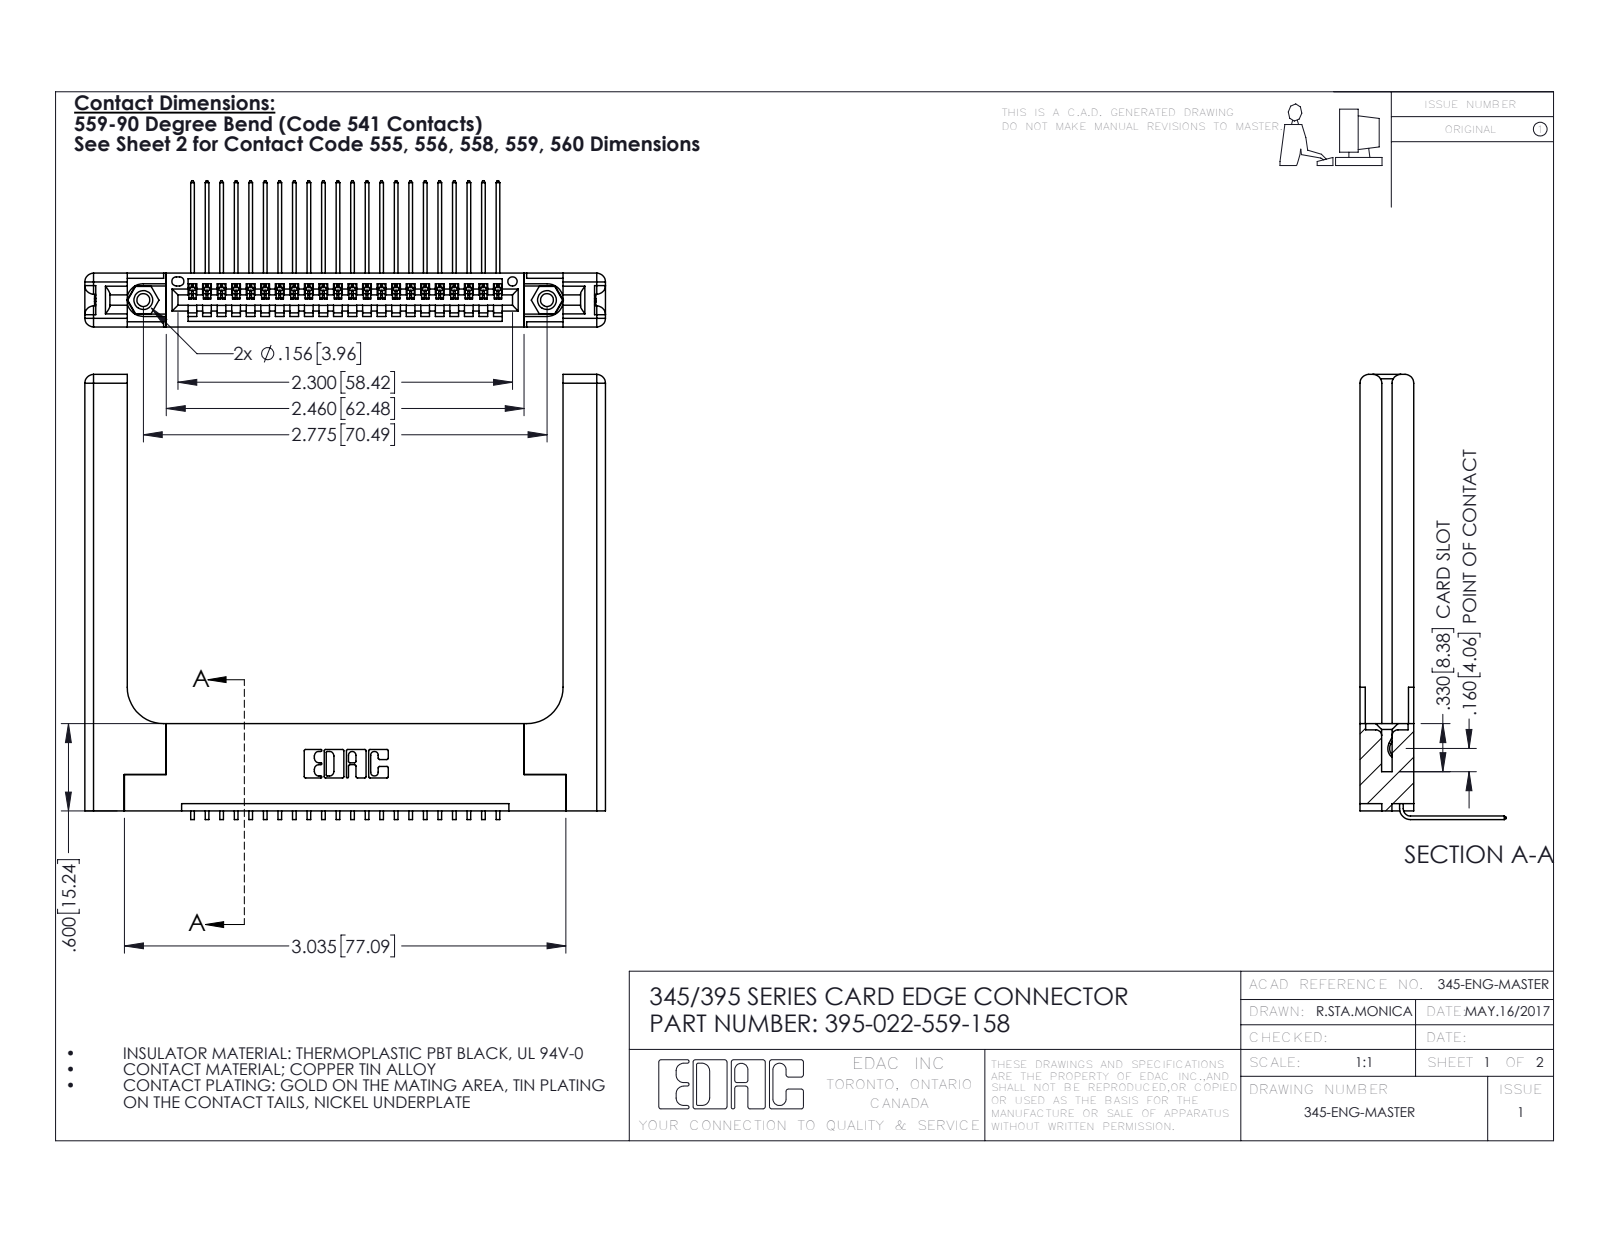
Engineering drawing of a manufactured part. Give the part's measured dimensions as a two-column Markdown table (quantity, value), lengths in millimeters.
| quantity | value |
| --- | --- |
| part name | 345-250-001_345-250-001-102; 395-022-559-158; 345-220-058_345-220-058; 345-292-001_558 559 Tail - 1 (+1 more) |
| STEP written by | SolidWorks 2016 (CONFIG_CONTROL_DESIGN) |
| units | millimeters |
| bodies | 27 solids, 1702 faces (1152 planar, 490 cylindrical, 60 other) |
| overall size | 90.9 × 77.7 × 25.5 |
| volume | 17 040 mm³ |
| surface area | 16 820 mm² |
| round holes (diameter × count) | 2.3 × 2, 3.2 × 2, 4 × 2, 1.6 × 1 |
| round bosses / shafts (diameter × count) | 3.9 × 2 |
| partial cylindrical surfaces (radius × count) | 0.2 × 44, 0.3 × 22, 1.5 × 16, 0.2 × 6, 0.8 × 6, 0.7 × 3, 0.8 × 2, 0.8 × 2 |
| main face-to-face distances | 9.4, 1.8, 7.6, 3.8, 3.8, 5.1, 2, 5.6, 2.5, 6.9 |
| hole center spacings | 6.9, 64.5, 70.5 |
